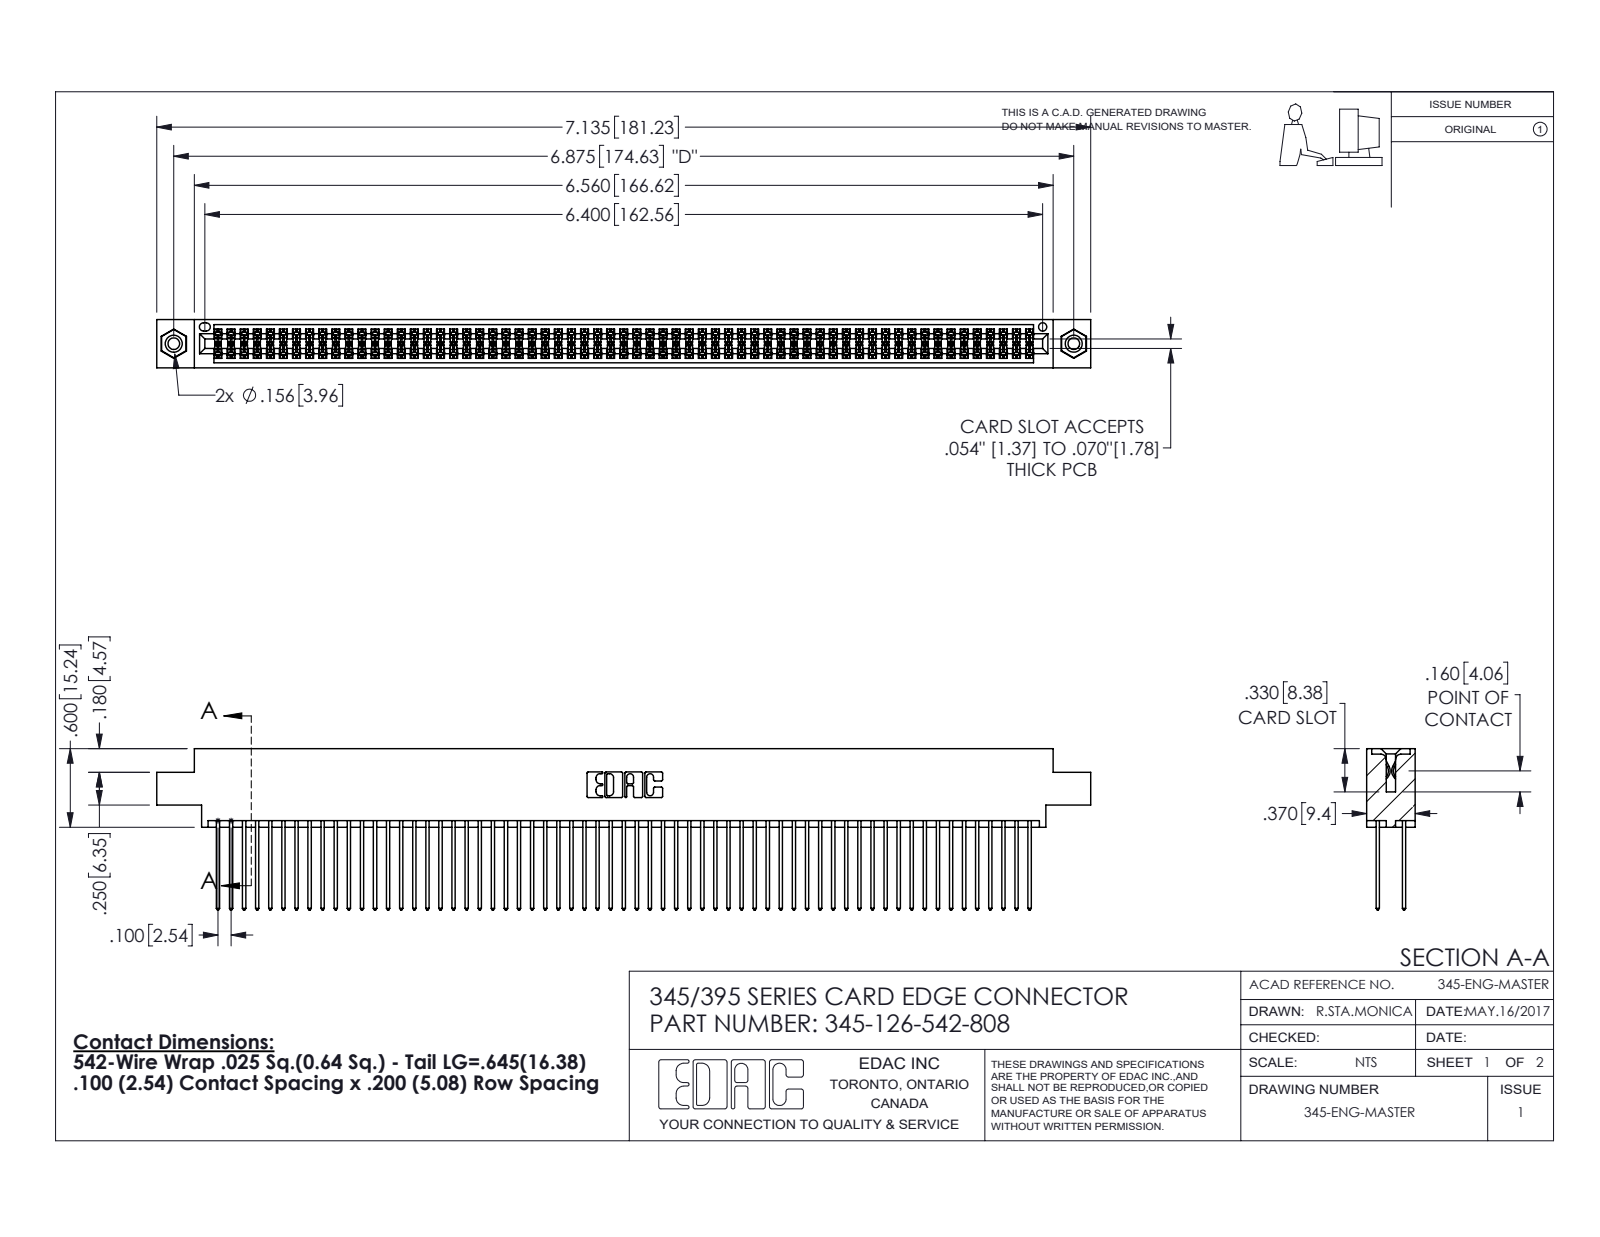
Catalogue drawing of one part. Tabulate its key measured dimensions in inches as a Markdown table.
| quantity | value |
| --- | --- |
| part name | 345-292-001_345-293-142; 345 Part_0.170 Offset - 0.156 Dia-TI; 345-126-542-808; 345-250-001_345-250-003-102 |
| STEP written by | SolidWorks 2016 (CONFIG_CONTROL_DESIGN) |
| units | inches |
| bodies | 129 solids, 6490 faces (4274 planar, 2200 cylindrical, 16 other) |
| overall size | 7.135 × 1.232 × 0.37 |
| volume | 1.115 in³ |
| surface area | 46.98 in² |
| round holes (diameter × count) | 0.089 × 2, 0.125 × 2, 0.156 × 2, 0.064 × 1 |
| round bosses / shafts (diameter × count) | 0.155 × 2 |
| partial cylindrical surfaces (radius × count) | 0.006 × 189, 0.01 × 126, 0.01 × 22, 0.007 × 6, 0.031 × 6, 0.026 × 3, 0.014 × 2, 0.019 × 2 |
| main face-to-face distances | 0.072, 0.298, 0.2, 0.098, 0.272, 0.025, 0.37, 0.225, 0.175, 0.149 |
| hole center spacings | 0.27, 6.639, 6.875 |
